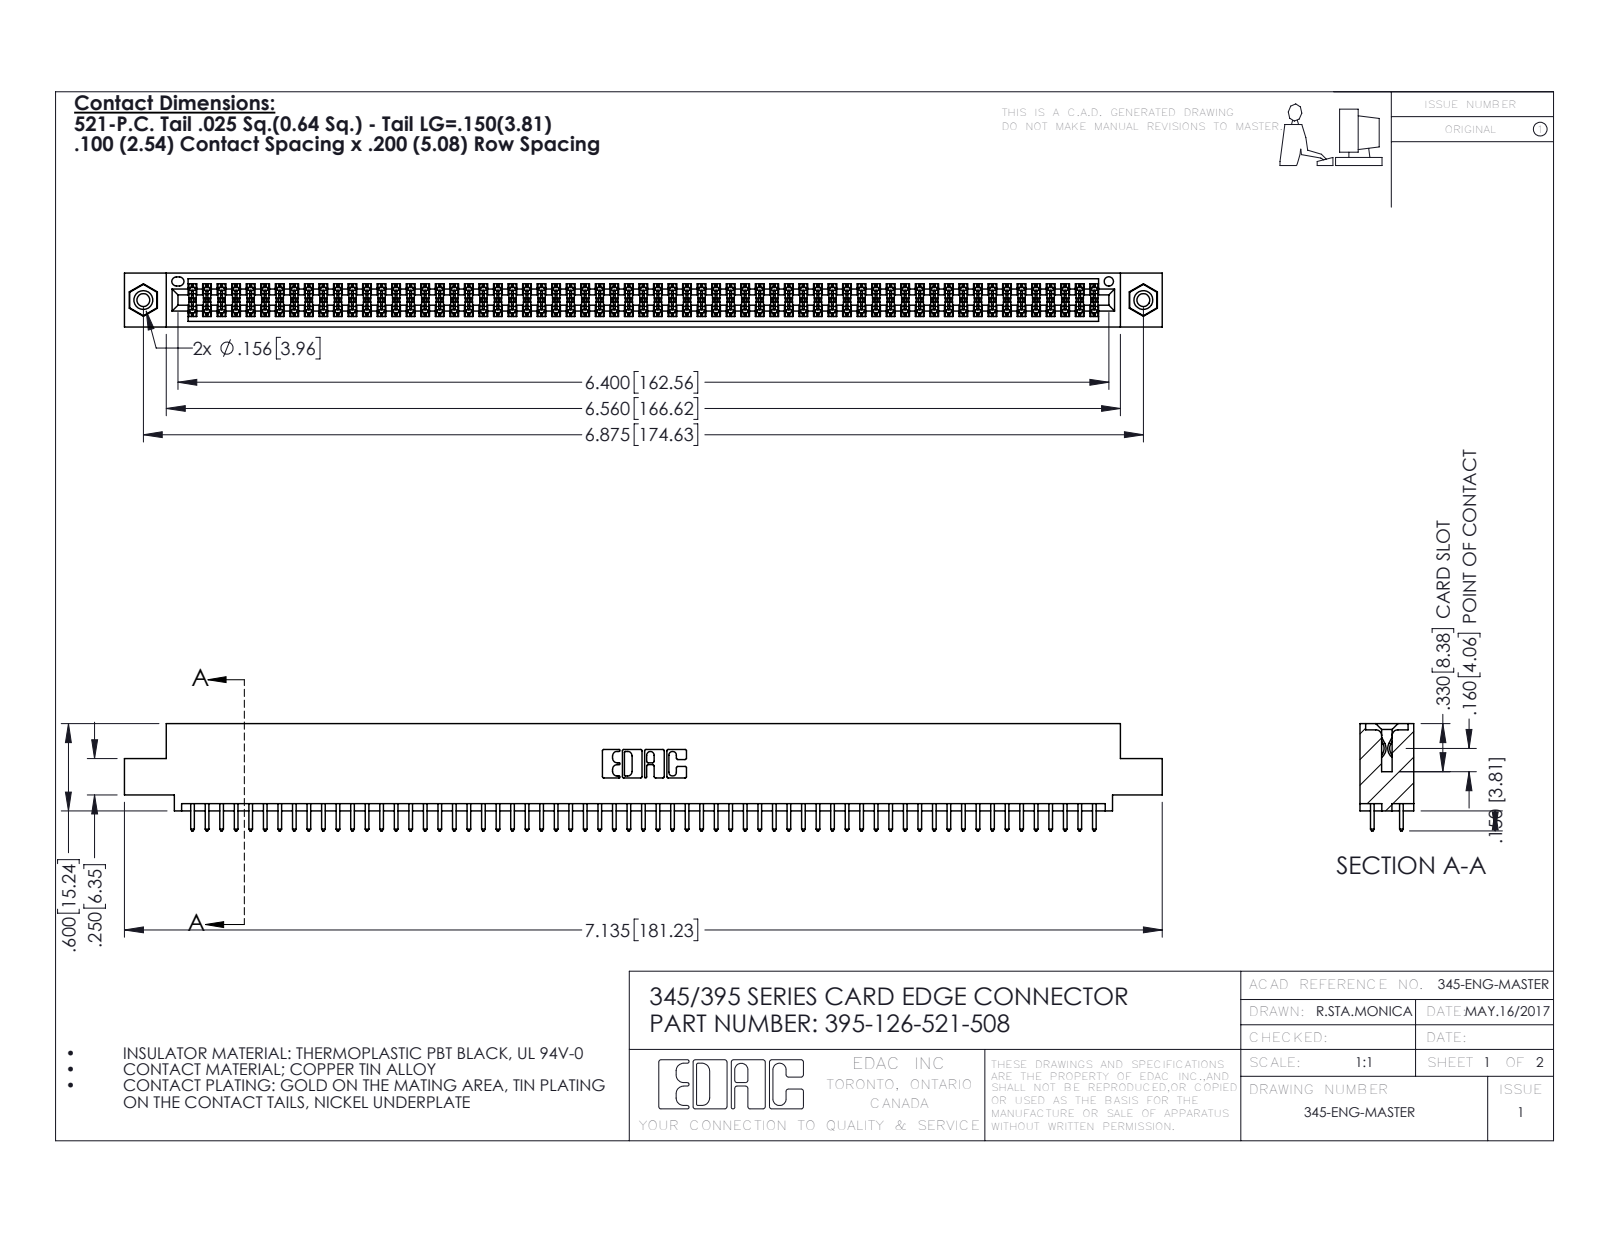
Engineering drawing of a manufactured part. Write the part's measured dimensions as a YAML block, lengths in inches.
part_name: "345-250-001_345-250-003-102; 345 Part_0.110 Offset - 0.156 Dia-TI; 395-126-521-508; 345-292-001_345-293-121"
step_written_by: "SolidWorks 2016 (CONFIG_CONTROL_DESIGN)"
units: inches
bodies: {solids: 129, faces: 6490, planar: 4274, cylindrical: 2200, other: 16}
overall_size: [7.135, 0.737, 0.37]
volume: 1.078
surface_area: 40.76
round_holes:
  - {diameter: 0.089, count: 2}
  - {diameter: 0.125, count: 2}
  - {diameter: 0.156, count: 2}
  - {diameter: 0.064, count: 1}
round_bosses_or_shafts:
  - {diameter: 0.155, count: 2}
partial_cylinders:
  - {radius: 0.006, count: 189}
  - {radius: 0.01, count: 126}
  - {radius: 0.01, count: 22}
  - {radius: 0.007, count: 6}
  - {radius: 0.031, count: 6}
  - {radius: 0.026, count: 3}
  - {radius: 0.014, count: 2}
  - {radius: 0.019, count: 2}
face_to_face_distances: [0.072, 0.298, 0.2, 0.098, 0.272, 0.025, 0.37, 0.225, 0.175, 0.149]
hole_center_spacings: [0.27, 6.639, 6.875]
